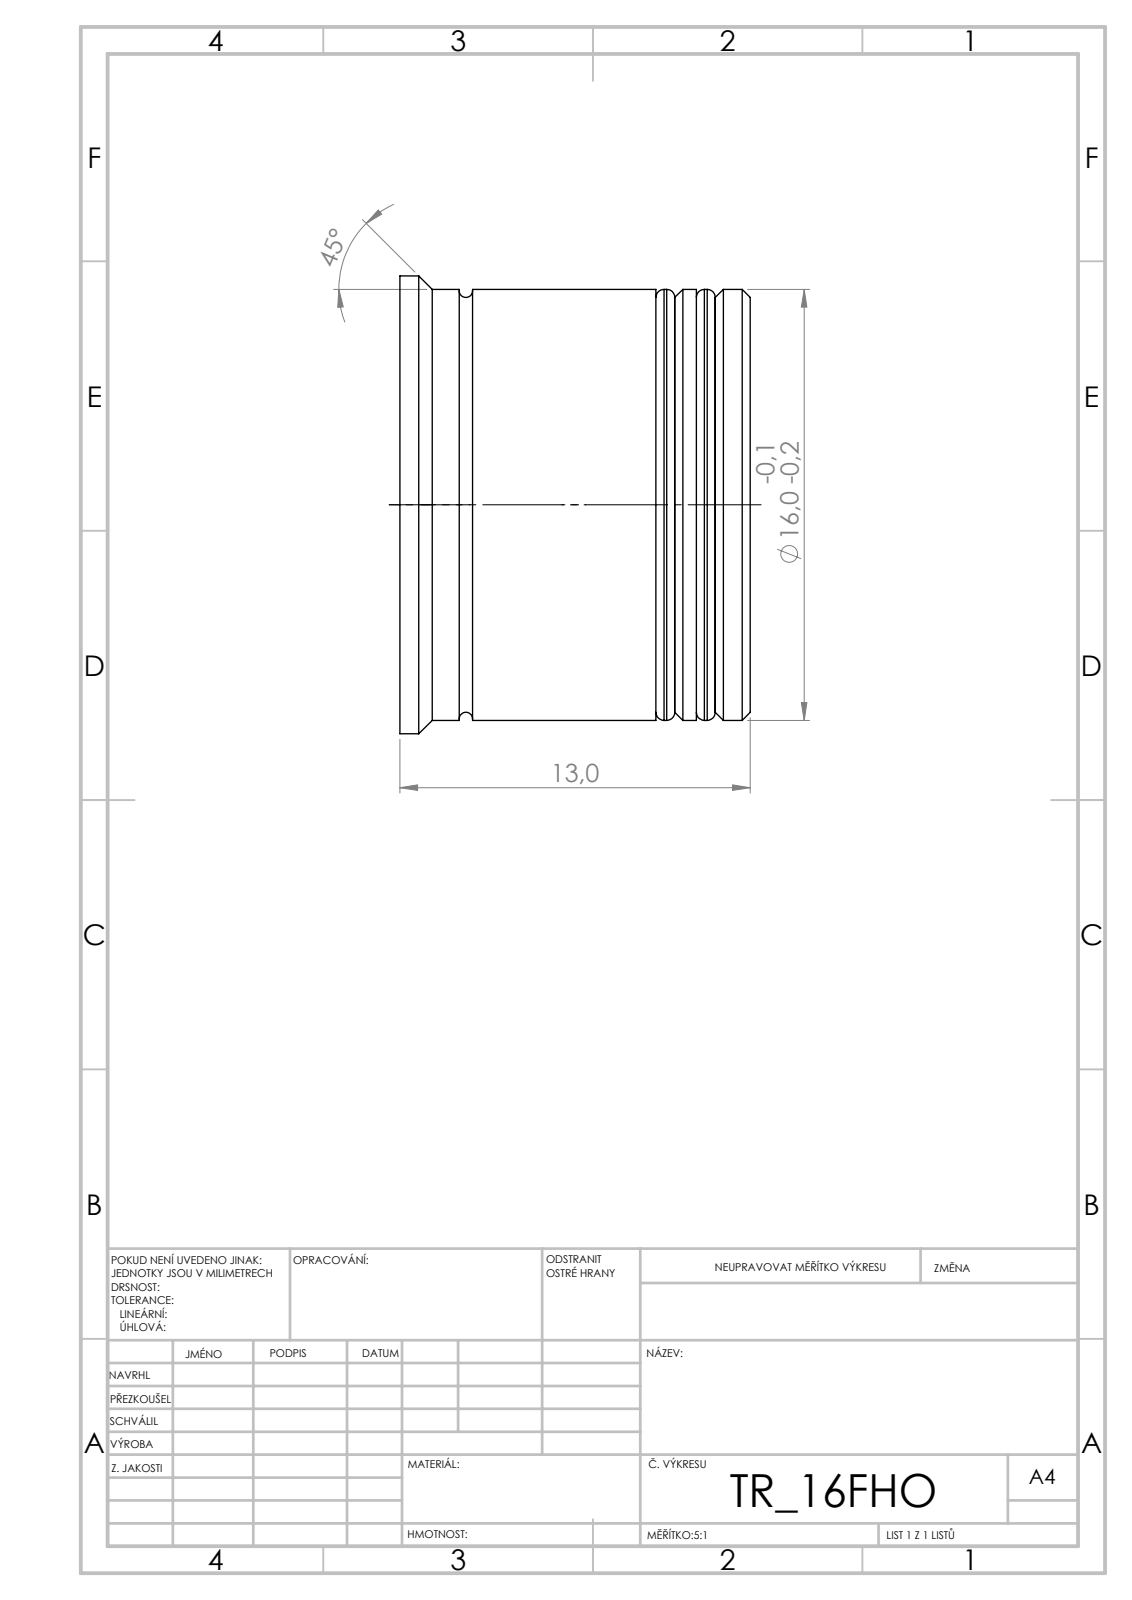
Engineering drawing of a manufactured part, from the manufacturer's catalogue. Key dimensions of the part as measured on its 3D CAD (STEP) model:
STEP written by: SolidWorks 2019 (CONFIG_CONTROL_DESIGN)
Units: millimetres
Bodies: 3 solids, 74 faces (29 planar, 25 cylindrical, 20 other)
Overall size (bounding box): 17 × 17 × 13
Volume: 2 723 mm³ · Surface area: 2 101 mm²
Round bosses / shafts (diameter × count): ⌀17 ×1, ⌀16 ×1, ⌀15.4 ×1
Partial cylindrical surfaces — rounded edges, fillets, slot ends (radius × count): R6.5 ×1
Main face-to-face distances: 1.5, 0.7, 2.2, 0.8, 1.3, 2, 2.8, 3.5, 12, 10.7
